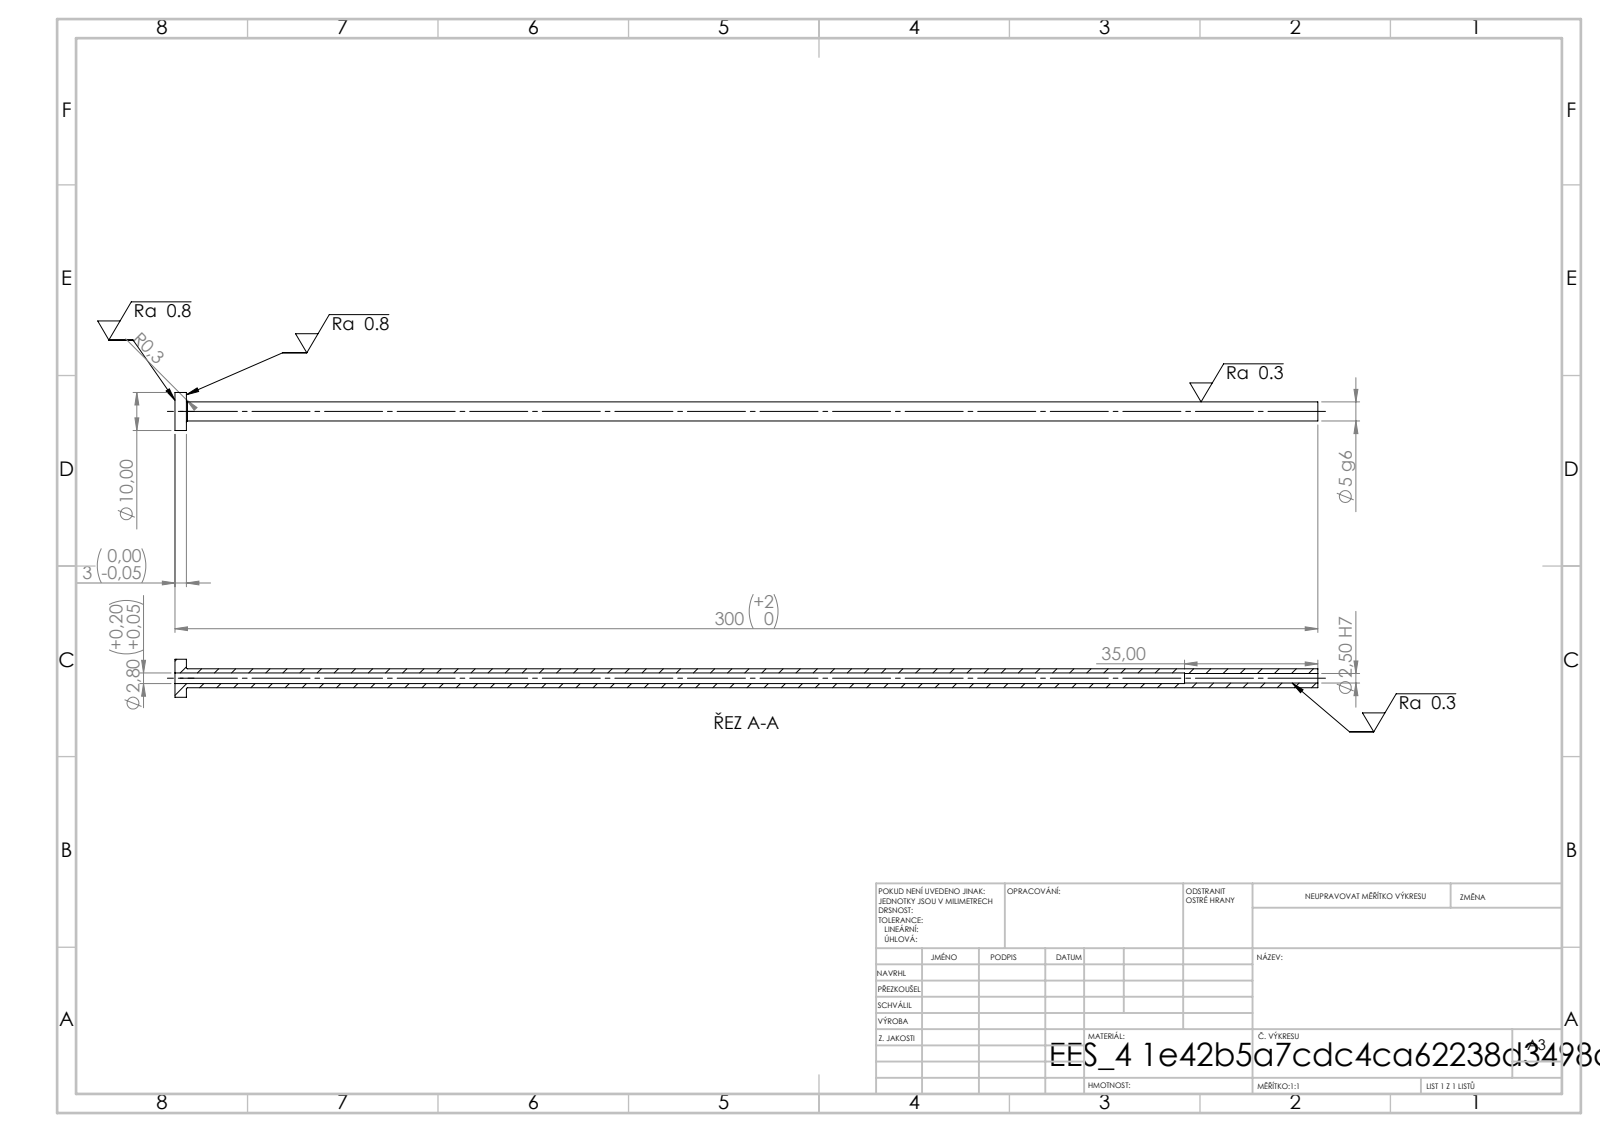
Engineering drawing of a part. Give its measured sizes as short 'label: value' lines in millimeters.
written by: SolidWorks 2019 (CONFIG_CONTROL_DESIGN)
unit: mm
bodies: 1 solid, 14 faces (4 planar, 8 cylindrical, 2 other)
size: 300 × 10 × 10
volume: 4 264 mm³; area: 7 511 mm²
holes: 1× ⌀2.5, 1× ⌀2.8
bosses: 1× ⌀10, 1× ⌀5
face distances: 3, 300, 297, 265, 262, 35
